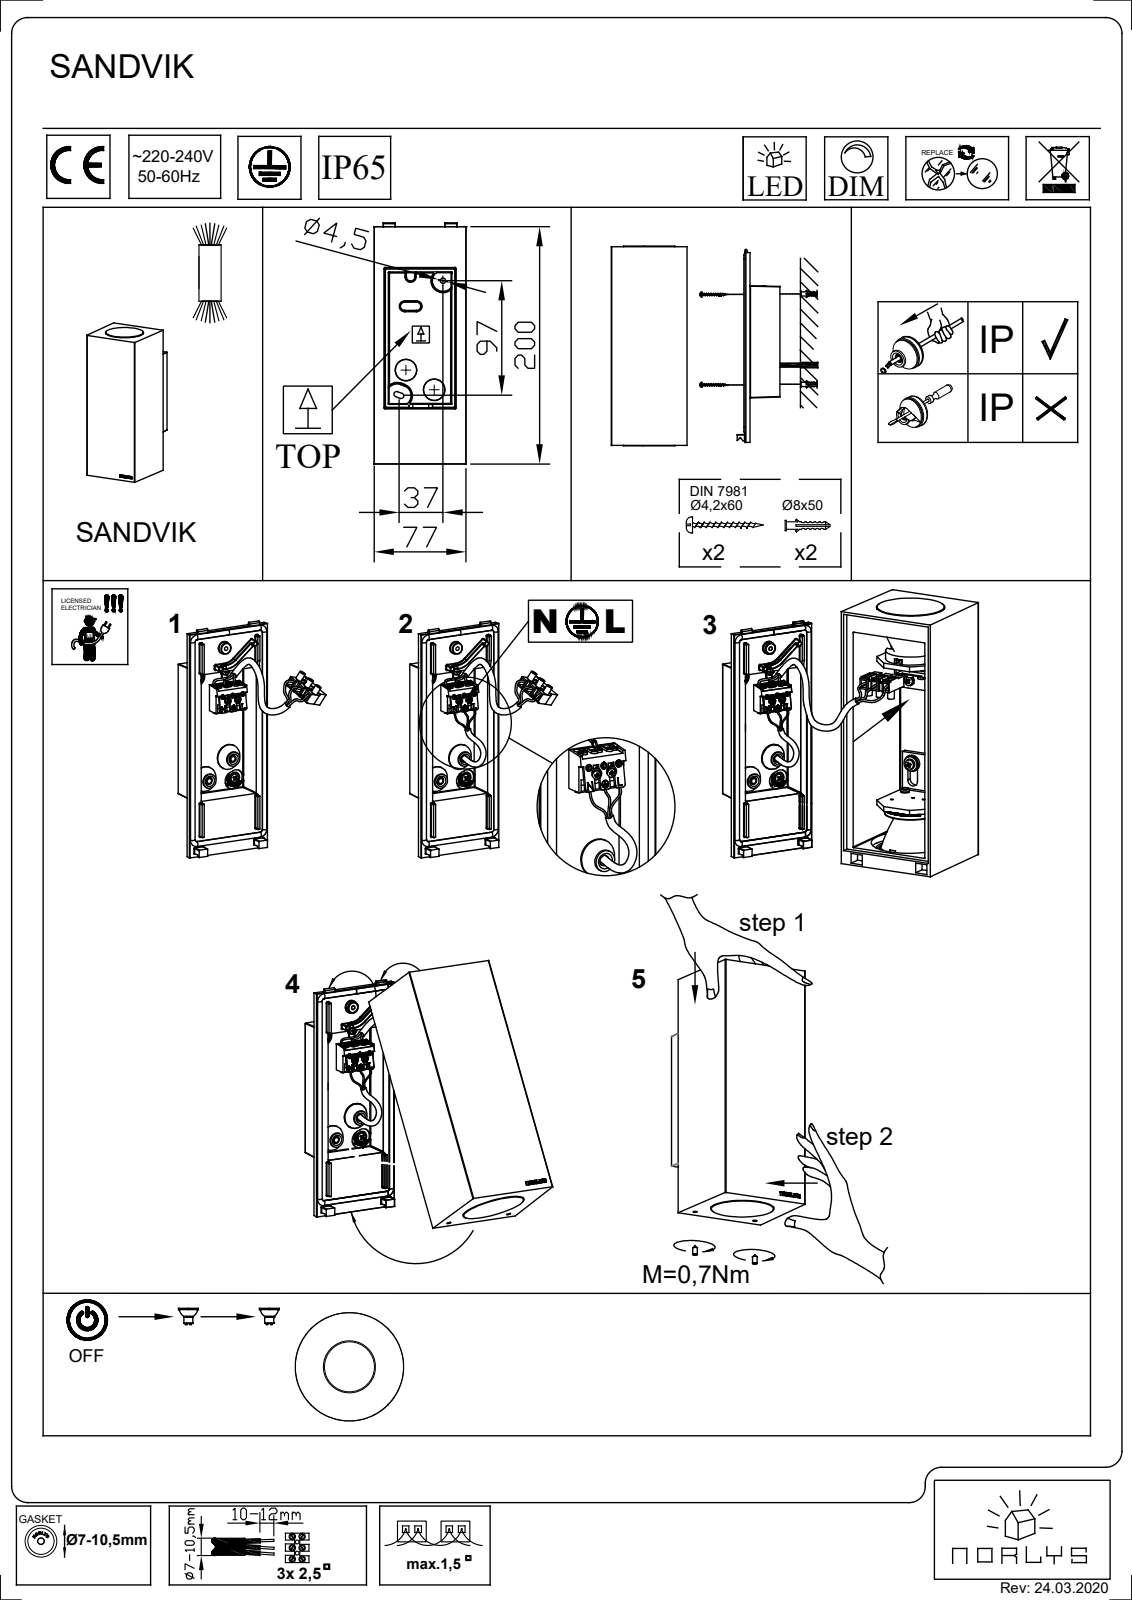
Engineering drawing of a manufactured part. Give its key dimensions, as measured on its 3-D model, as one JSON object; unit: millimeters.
{"step_written_by": "ACIS (automotive_design)", "units": "millimeters", "bodies": {"solids": 2, "faces": 35, "planar": 9, "cylindrical": 16, "other": 10}, "overall_size": [130, 26, 26], "volume_mm3": 50346, "surface_area_mm2": 16543, "round_holes": [[21.94, 1]], "round_bosses_or_shafts": [[26, 1], [20, 1]], "partial_cylinders_radius": [[1.44, 1], [2.37, 1], [3.26, 1], [9.99, 1]], "face_to_face_distances": [45, 130, 85, 0.92, 95.24, 50.24, 34.76]}
